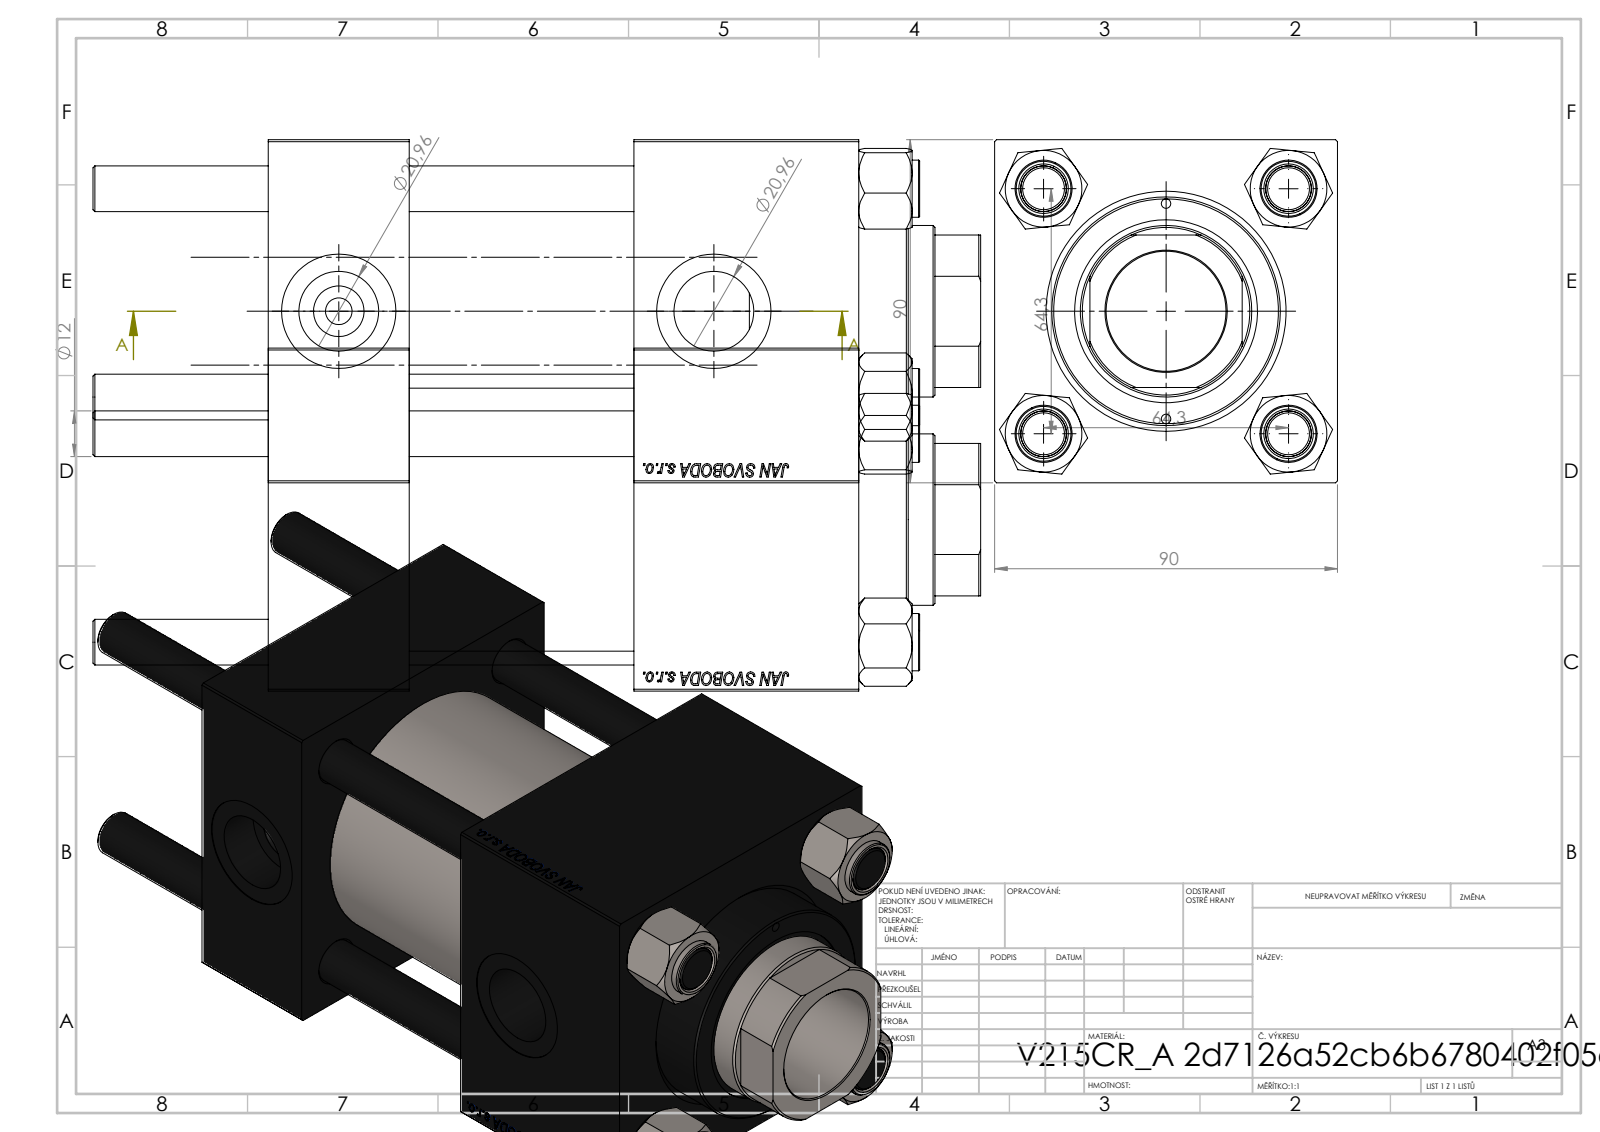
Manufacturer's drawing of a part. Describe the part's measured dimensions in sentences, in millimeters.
The part is named "V215CR_VCP; CR025_012_A_0_G_A_G_M_020_+#_##_TYCINKA; NUT_M5; V215_VC_A (+1 more)". Its 3-D file was written by "SolidWorks 2019 (CONFIG_CONTROL_DESIGN)". It is 11 solids with 1137 faces: 520 planar, 81 cylindrical and 536 other. Overall it measures 233 by 90 by 90 millimeters. Its volume is 1 031 000 cubic millimeters and its surface area 206 804 square millimeters. Round holes: 4 of diameter 12, 2 of diameter 2.5, 2 of diameter 7, 2 of diameter 20.96, 2 of diameter 30, 1 of diameter 31.5, 1 of diameter 45, 1 of diameter 48, 1 of diameter 50, 1 of diameter 60, 1 of diameter 63. Round bosses or shafts: 4 of diameter 15, 1 of diameter 69. Partial cylindrical surfaces (rounded edges, fillets, slot ends): 1 of radius 22. The main face-to-face distances are 90, 59, 37, 155, 118, 96, 126.3, 89.3, 30.3, 28.7. The hole center spacings are 32.39, 45.47, 64.3, 68.42, 28.25, 90.93, 56.5, 98.46.
